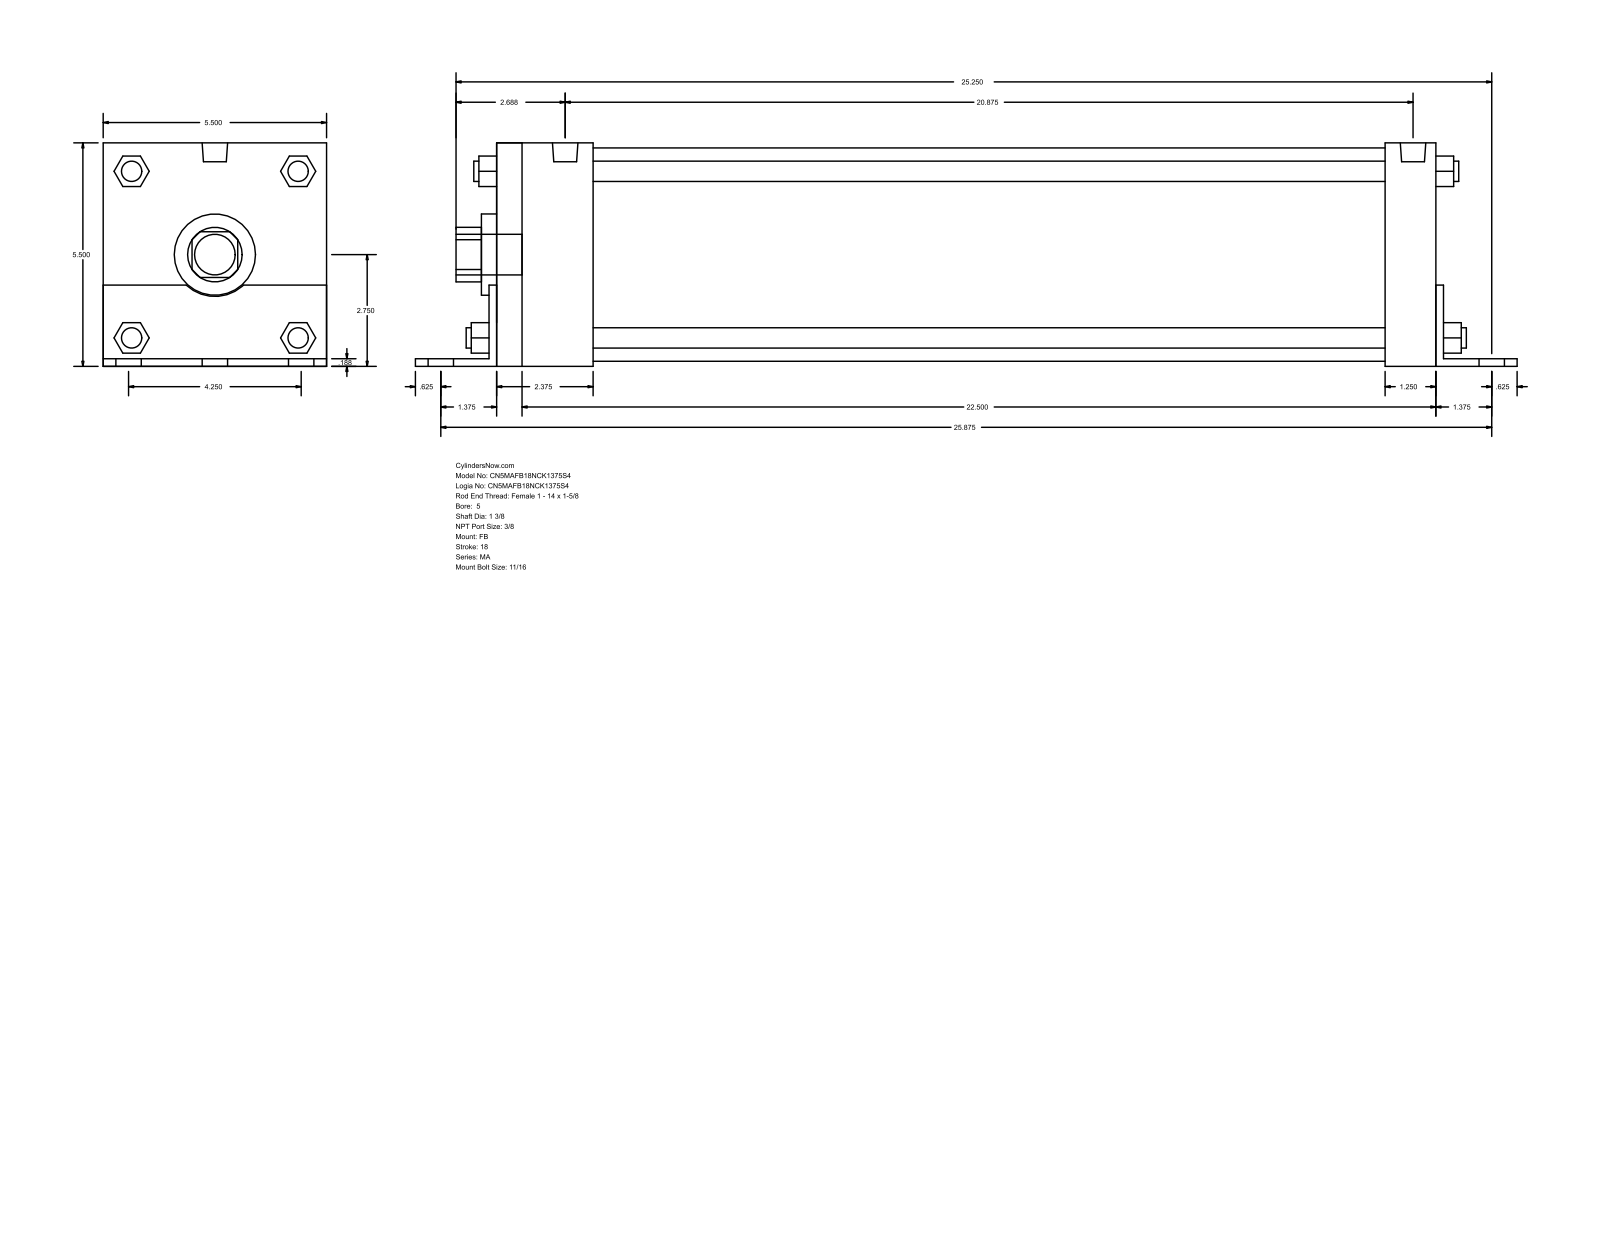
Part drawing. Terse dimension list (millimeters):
name: MA_FB__0500_1.375
written by: GSSL Pune (CONFIG_CONTROL_DESIGN)
unit: mm
bodies: 0 solids, 140 faces (105 planar, 35 cylindrical, 0 other)
size: 688.98 × 139.75 × 139.7
holes: 1× ⌀34.92, 1× ⌀50.8, 1× ⌀133.35
bosses: 6× ⌀17.46, 4× ⌀12.7, 4× ⌀11.11, 2× ⌀15.93, 1× ⌀25.4
rounds: 1× R17.06, 1× R26.16
face distances: 139.7, 4.76, 139.75, 4.71, 134.99, 587.37, 4.77, 592.14, 592.13, 596.9
